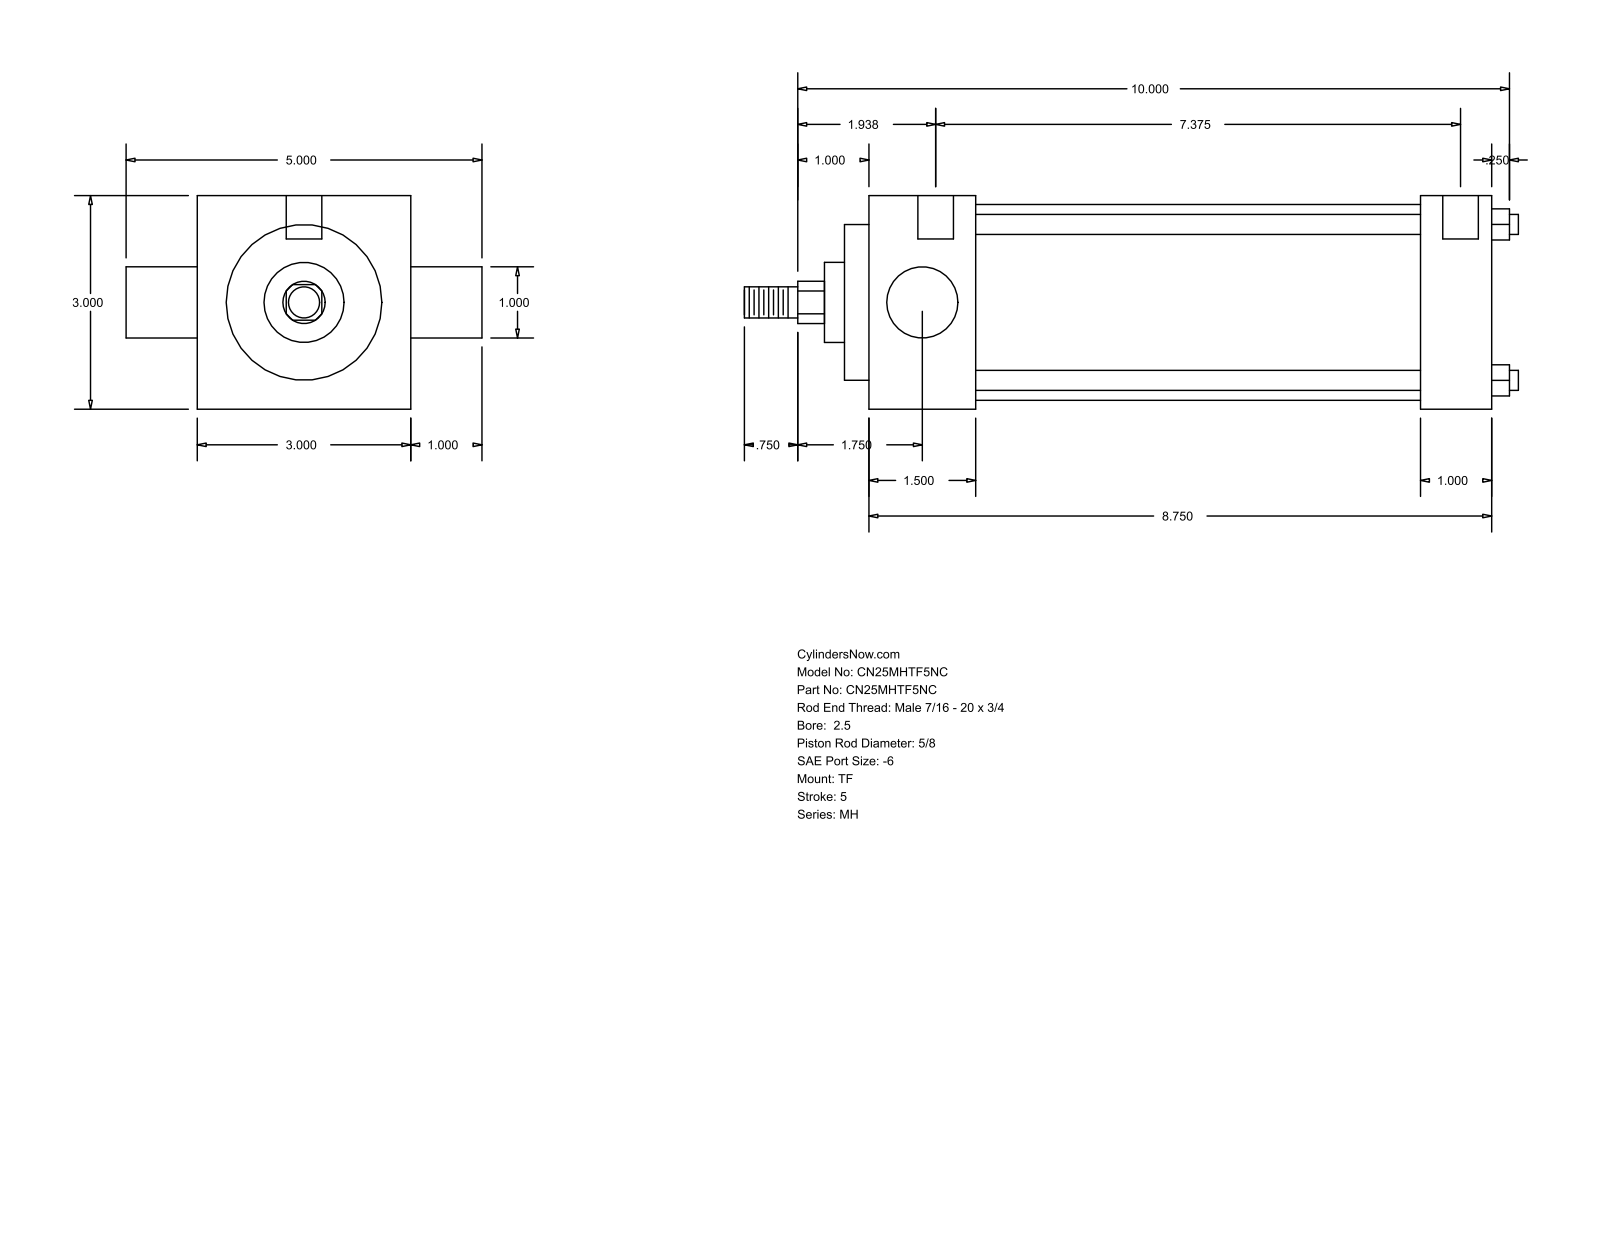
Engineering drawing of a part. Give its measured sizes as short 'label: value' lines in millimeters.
name: MH_TF__0250_0.625
written by: GSSL Pune (CONFIG_CONTROL_DESIGN)
unit: mm
bodies: 0 solids, 86 faces (61 planar, 25 cylindrical, 0 other)
size: 276.23 × 127 × 76.2
holes: 3× ⌀5.56, 2× ⌀12.7
bosses: 4× ⌀7.14, 1× ⌀69.85, 1× ⌀55.55, 1× ⌀28.57, 1× ⌀25.4, 1× ⌀15.88, 1× ⌀11.11
rounds: 1× R7.54
face distances: 76.2, 222.25, 25.4, 38.1, 184.15, 196.85, 158.75, 8.73, 46.83, 205.58
hole spacings: 3.17, 4.76, 187.33, 190.5, 192.09, 195.26
